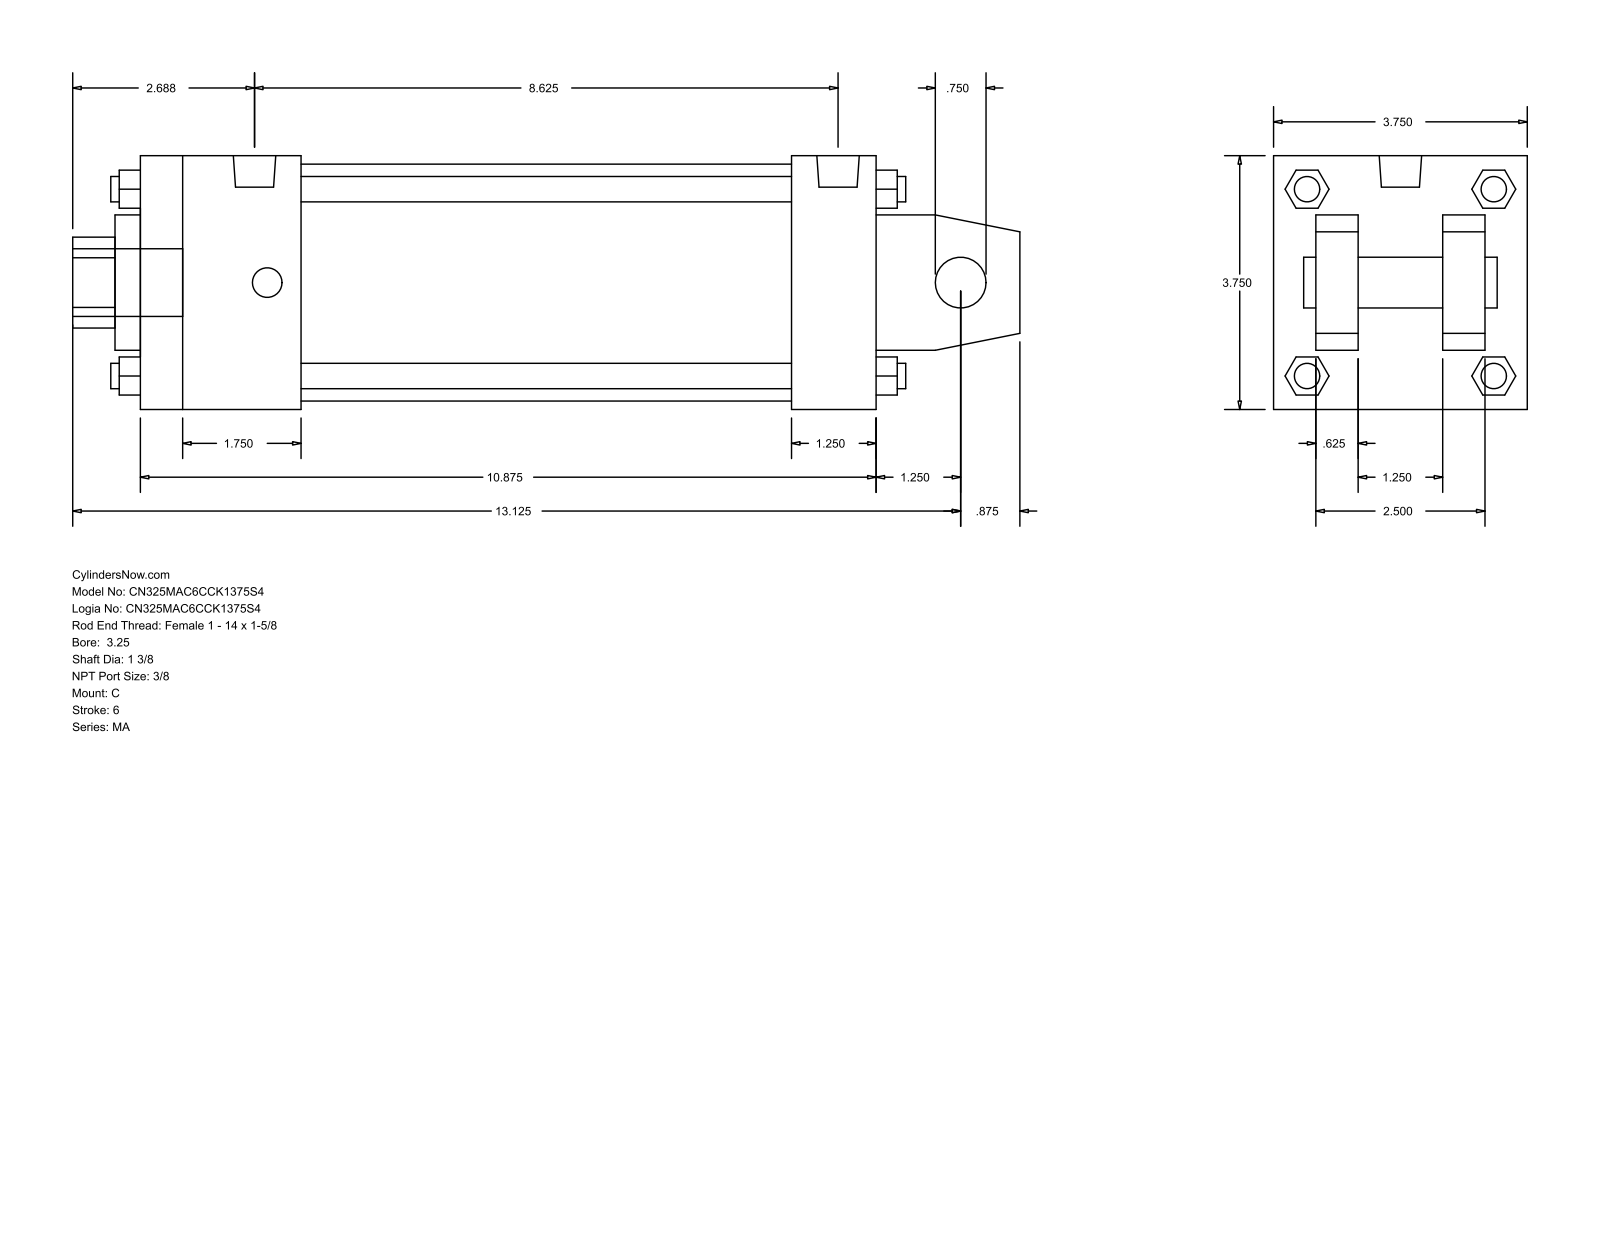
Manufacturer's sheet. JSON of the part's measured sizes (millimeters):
{"part_name": "MA_C__0325_1.375", "step_written_by": "GSSL Pune (CONFIG_CONTROL_DESIGN)", "units": "millimeters", "bodies": {"solids": 0, "faces": 139, "planar": 108, "cylindrical": 31, "other": 0}, "overall_size": [355.6, 95.25, 95.25], "round_holes": [[19.05, 1], [34.92, 1], [50.8, 1], [88.9, 1]], "round_bosses_or_shafts": [[11.11, 4], [9.53, 4], [15.93, 2], [25.4, 1]], "partial_cylinders_radius": [[17.06, 1]], "face_to_face_distances": [95.24, 15.87, 31.74, 63.5, 276.22, 79.37, 47.63, 244.48, 60.32, 184.16]}
